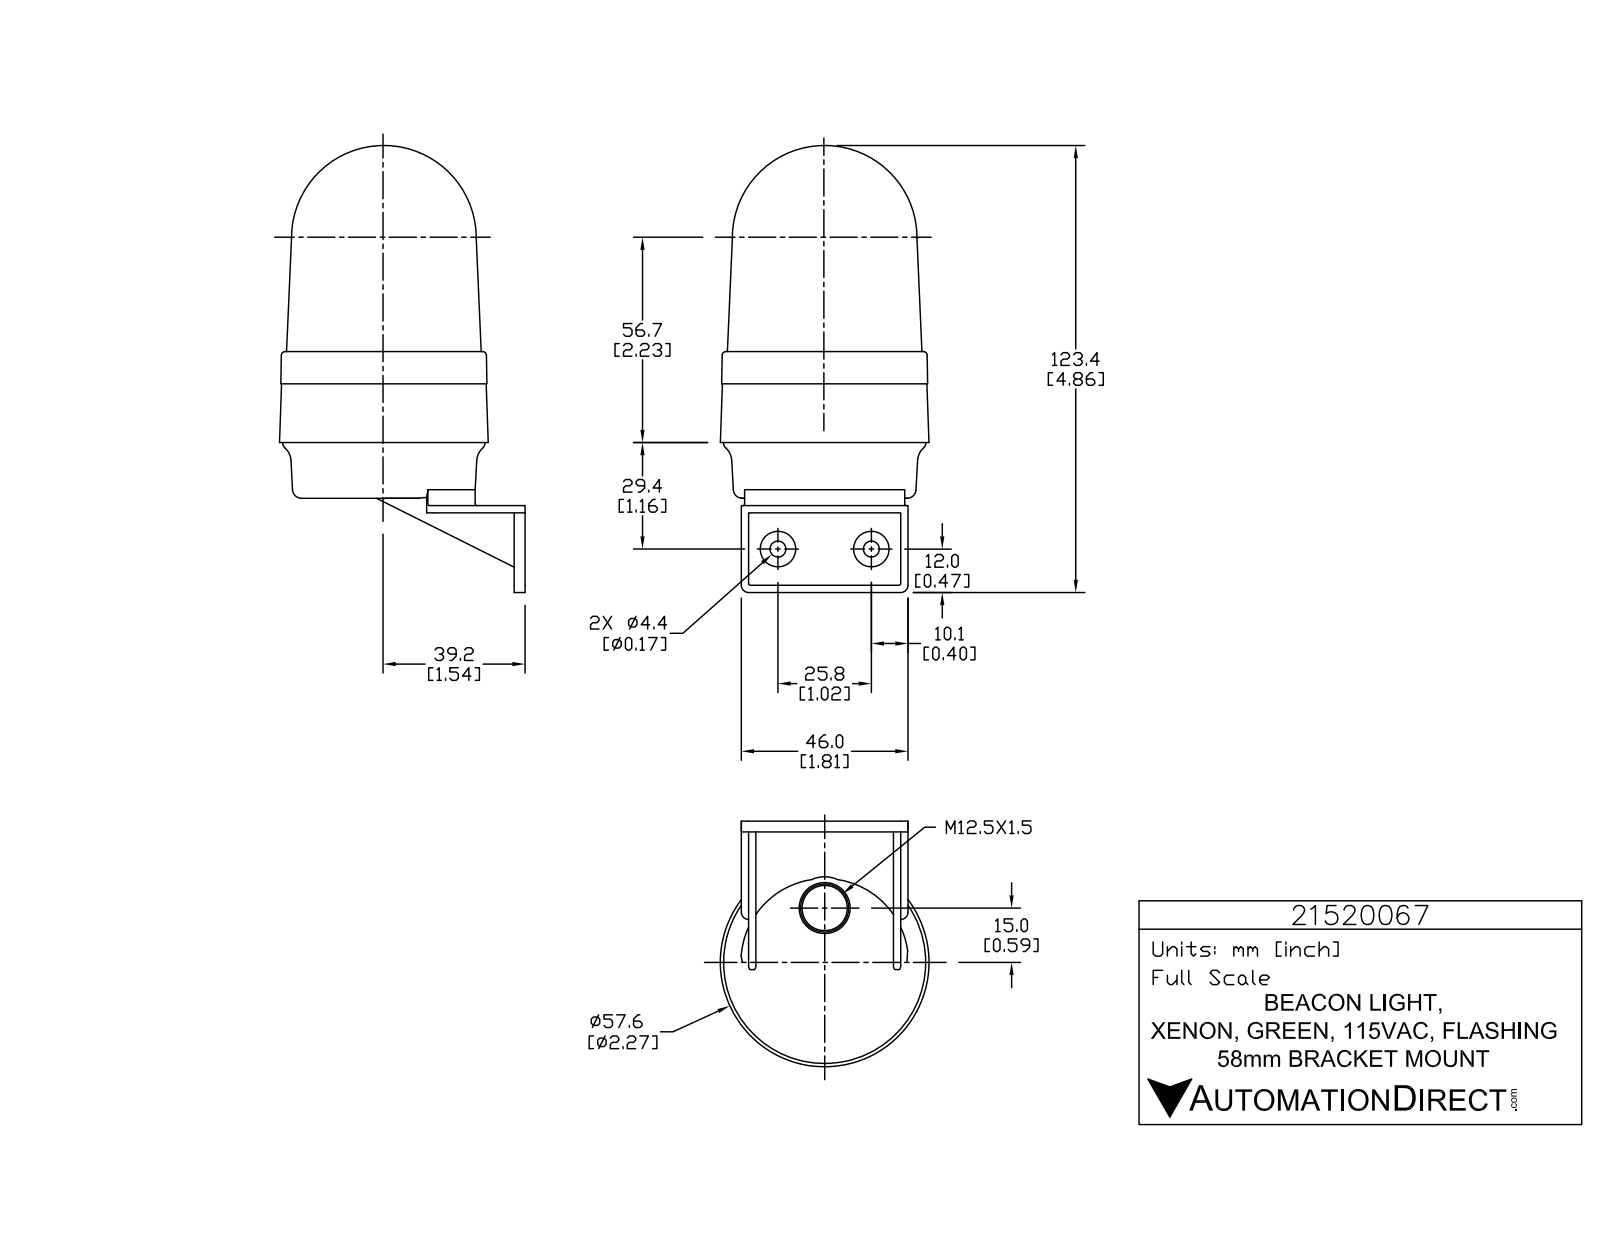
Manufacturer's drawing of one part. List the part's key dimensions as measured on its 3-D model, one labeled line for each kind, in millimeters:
Part name (STEP PRODUCT): 21520067
STEP written by: SolidWorks 2015 (AUTOMOTIVE_DESIGN)
Units: millimetres
Bodies: 1 solid, 828 faces (551 planar, 179 cylindrical, 98 other)
Overall size (bounding box): 123.4 × 72.4 × 61.1
Volume: 203 700 mm³ · Surface area: 24 190 mm²
Round holes (diameter × count): ⌀1 ×3, ⌀4.4 ×2
Round bosses / shafts (diameter × count): ⌀5.7 ×3, ⌀1.4 ×3, ⌀9.8 ×2, ⌀55.8 ×1
Partial cylindrical surfaces — rounded edges, fillets, slot ends (radius × count): R0.2 ×6, R0.2 ×6, R0.2 ×6, R0.5 ×6, R3.3 ×6, R2 ×4, R0.1 ×3, R0.1 ×3
Main face-to-face distances: 2, 4, 40, 42, 1, 3, 38, 22, 24, 19.4
Hole centre spacings: 25.8
